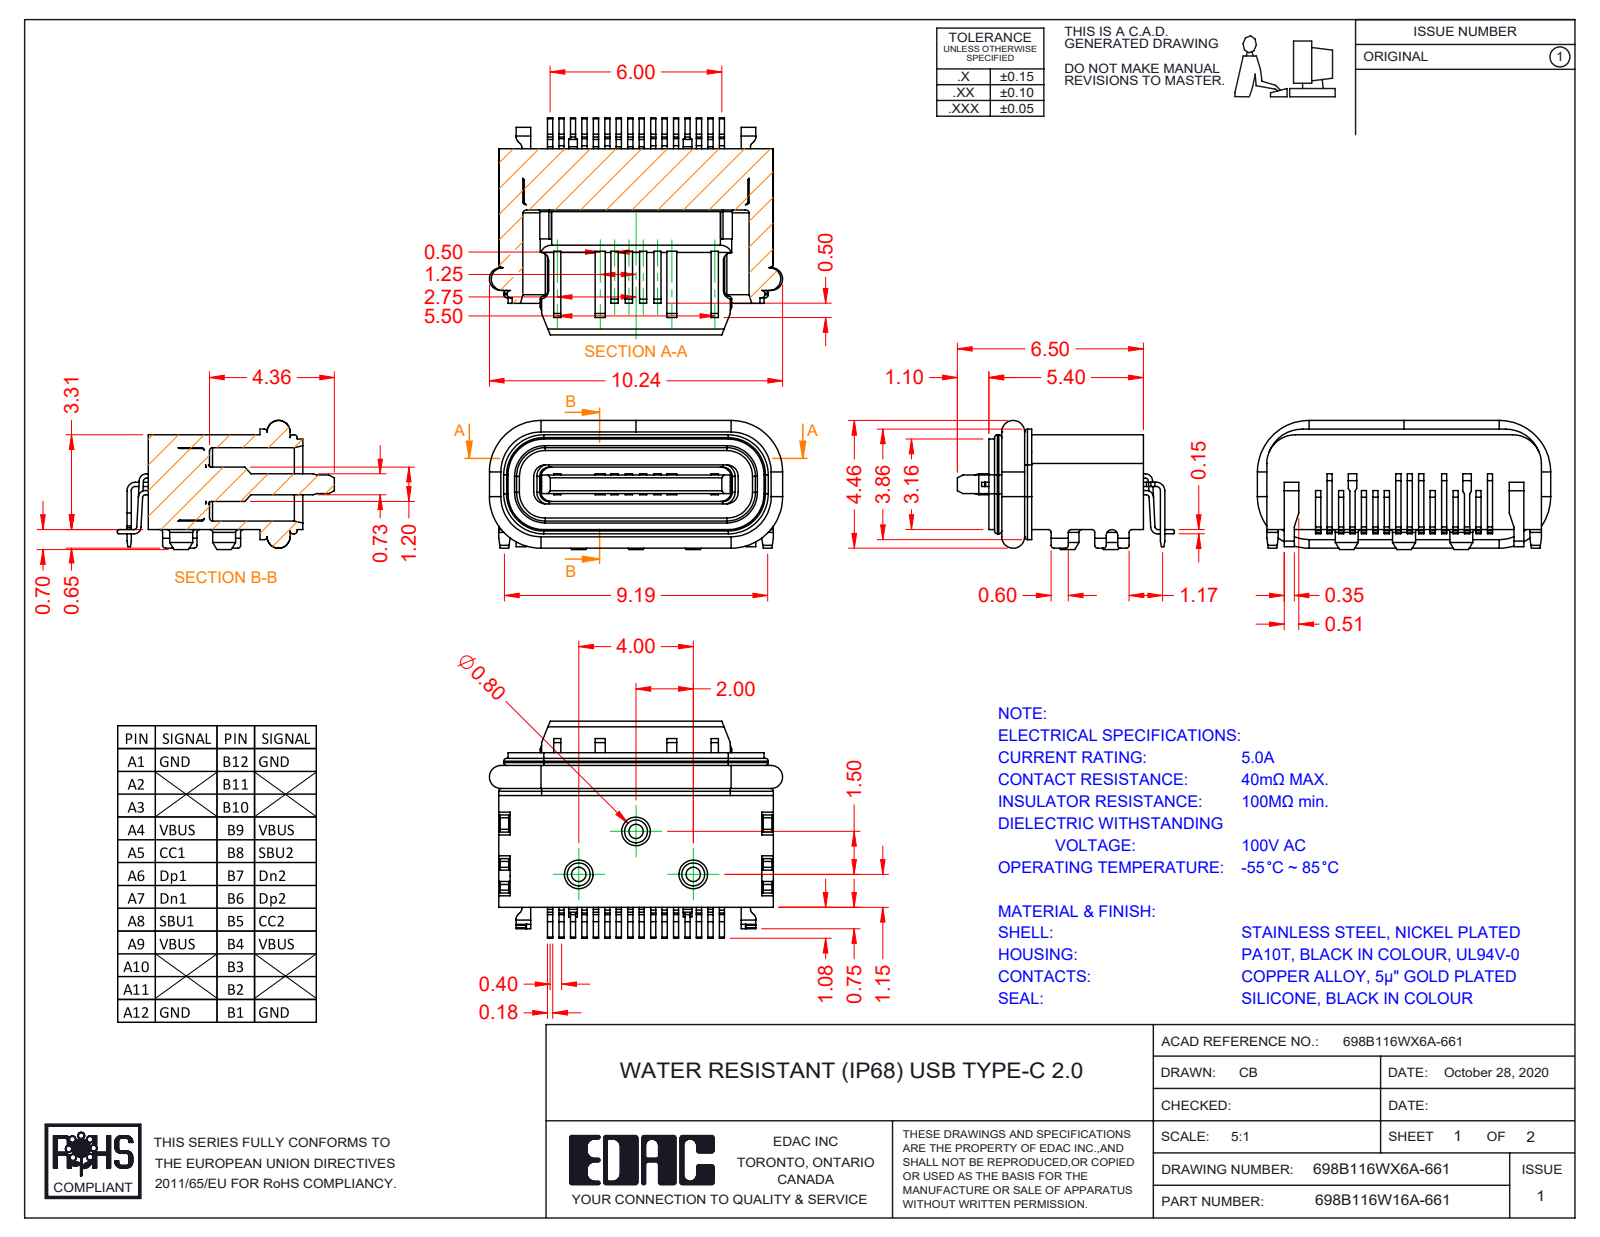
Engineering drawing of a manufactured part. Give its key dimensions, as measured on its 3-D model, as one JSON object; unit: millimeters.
{"part_name": "698B116W16A-661 - EDAC USB Connector", "step_written_by": "SolidWorks 2020 (AUTOMOTIVE_DESIGN)", "units": "millimeters", "bodies": {"solids": 1, "faces": 678, "planar": 420, "cylindrical": 200, "other": 58}, "overall_size": [10.24, 7.58, 4.51], "volume_mm3": 135, "surface_area_mm2": 430, "round_holes": [[0.9, 2]], "round_bosses_or_shafts": [[0.8, 3], [0.6, 2]], "partial_cylinders_radius": [[0.1, 41], [0.4, 12], [0.2, 11], [1, 10], [1.25, 6], [0.3, 5], [0.32, 4], [1.4, 4]], "face_to_face_distances": [3.31, 0.45, 0.96, 1.6, 3.01, 2.86, 2.56, 0.68, 0.92, 1.9], "hole_center_spacings": [5]}
